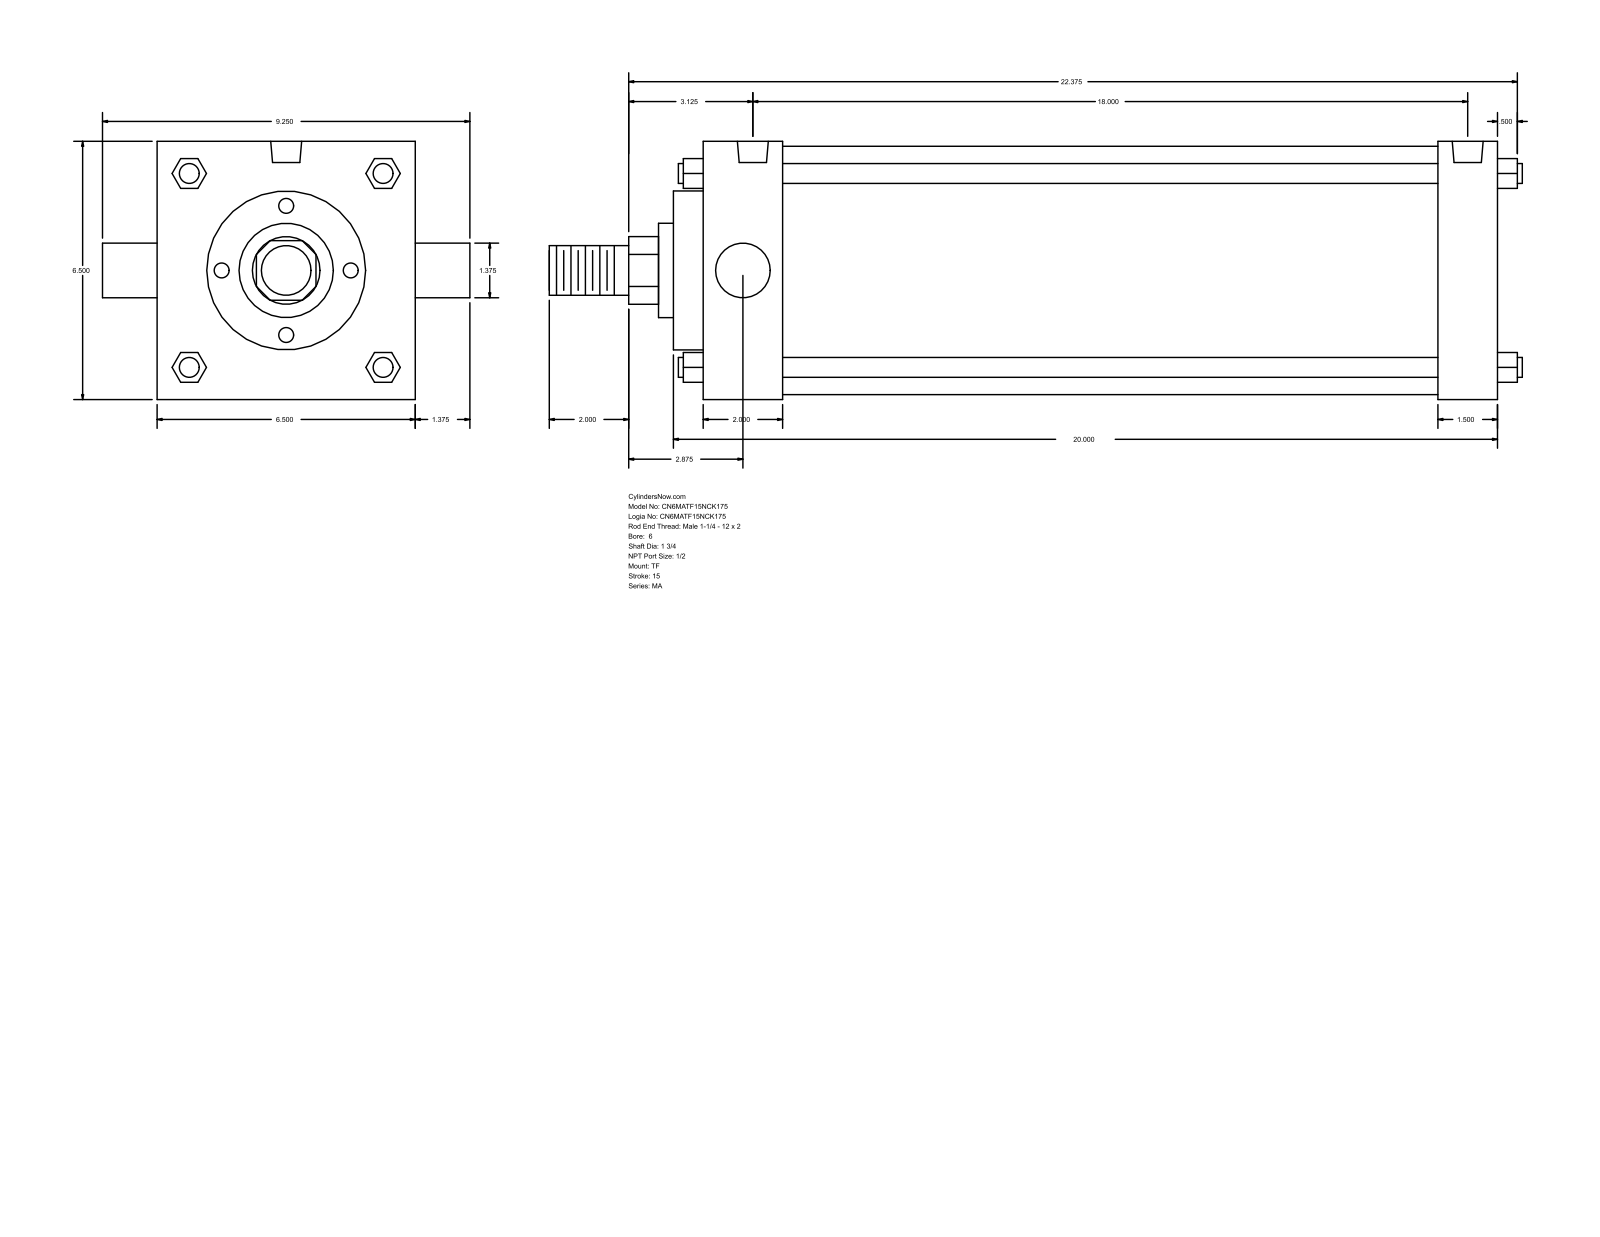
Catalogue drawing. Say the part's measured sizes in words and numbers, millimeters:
The part is named "MA_TF__0600_1.75". Its 3-D file was written by "GSSL Pune (CONFIG_CONTROL_DESIGN)". It is 0 solids with 122 faces: 93 planar, 29 cylindrical and 0 other. Overall it measures 622.3 by 234.95 by 165.1 millimeters. Round holes: 3 of diameter 17.46, 2 of diameter 19.77. Round bosses or shafts: 4 of diameter 12.7, 1 of diameter 158.75, 1 of diameter 101.6, 1 of diameter 60.33, 1 of diameter 44.45, 1 of diameter 34.92, 1 of diameter 31.75. Partial cylindrical surfaces (rounded edges, fillets, slot ends): 1 of radius 21.63. The main face-to-face distances are 165.1, 508, 19.05, 38.1, 50.8, 457.2, 469.9, 419.1, 69.85, 488.95. The hole center spacings are 457.2.
